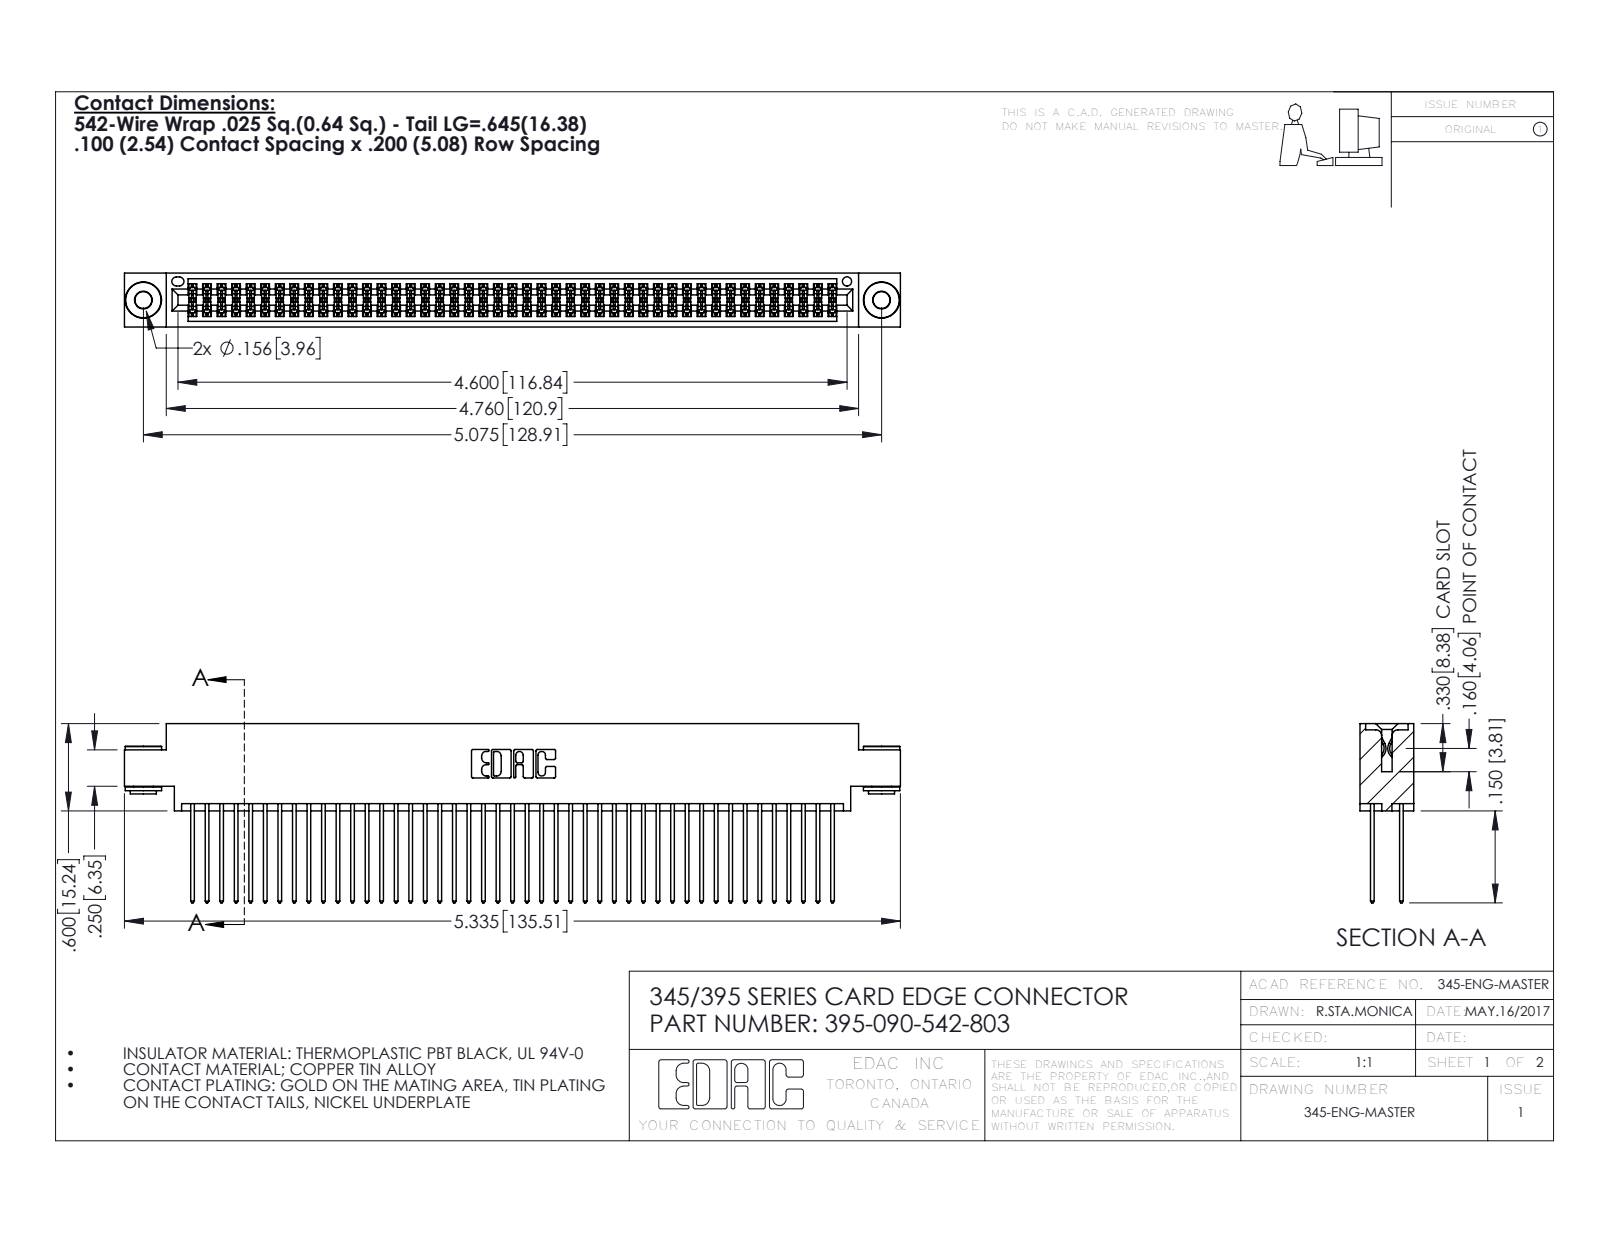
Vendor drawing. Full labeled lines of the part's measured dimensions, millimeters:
Part name (STEP PRODUCT): 345-250-002_345-250-002-102; 395-090-542-803; 345-292-001_345-293-142; 345 Part_0.170 Offset - 0.156 Dia-TH
STEP written by: SolidWorks 2016 (CONFIG_CONTROL_DESIGN)
Units: millimetres
Bodies: 93 solids, 4668 faces (3064 planar, 1596 cylindrical, 8 other)
Overall size (bounding box): 135.5 × 31.3 × 9.4
Volume: 13 500 mm³ · Surface area: 22 350 mm²
Round holes (diameter × count): ⌀2.9 ×2, ⌀4 ×2, ⌀1.6 ×1
Round bosses / shafts (diameter × count): ⌀6.4 ×2, ⌀4.6 ×2, ⌀3.5 ×2
Partial cylindrical surfaces — rounded edges, fillets, slot ends (radius × count): R0.2 ×135, R0.3 ×90, R0.3 ×22, R0.2 ×6, R0.8 ×6, R0.7 ×3, R0.4 ×2, R0.5 ×2
Main face-to-face distances: 1.8, 7.6, 5.1, 2.5, 6.9, 0.6, 9.4, 5.7, 4.4, 3.8
Hole centre spacings: 6.9, 122.9, 128.9
